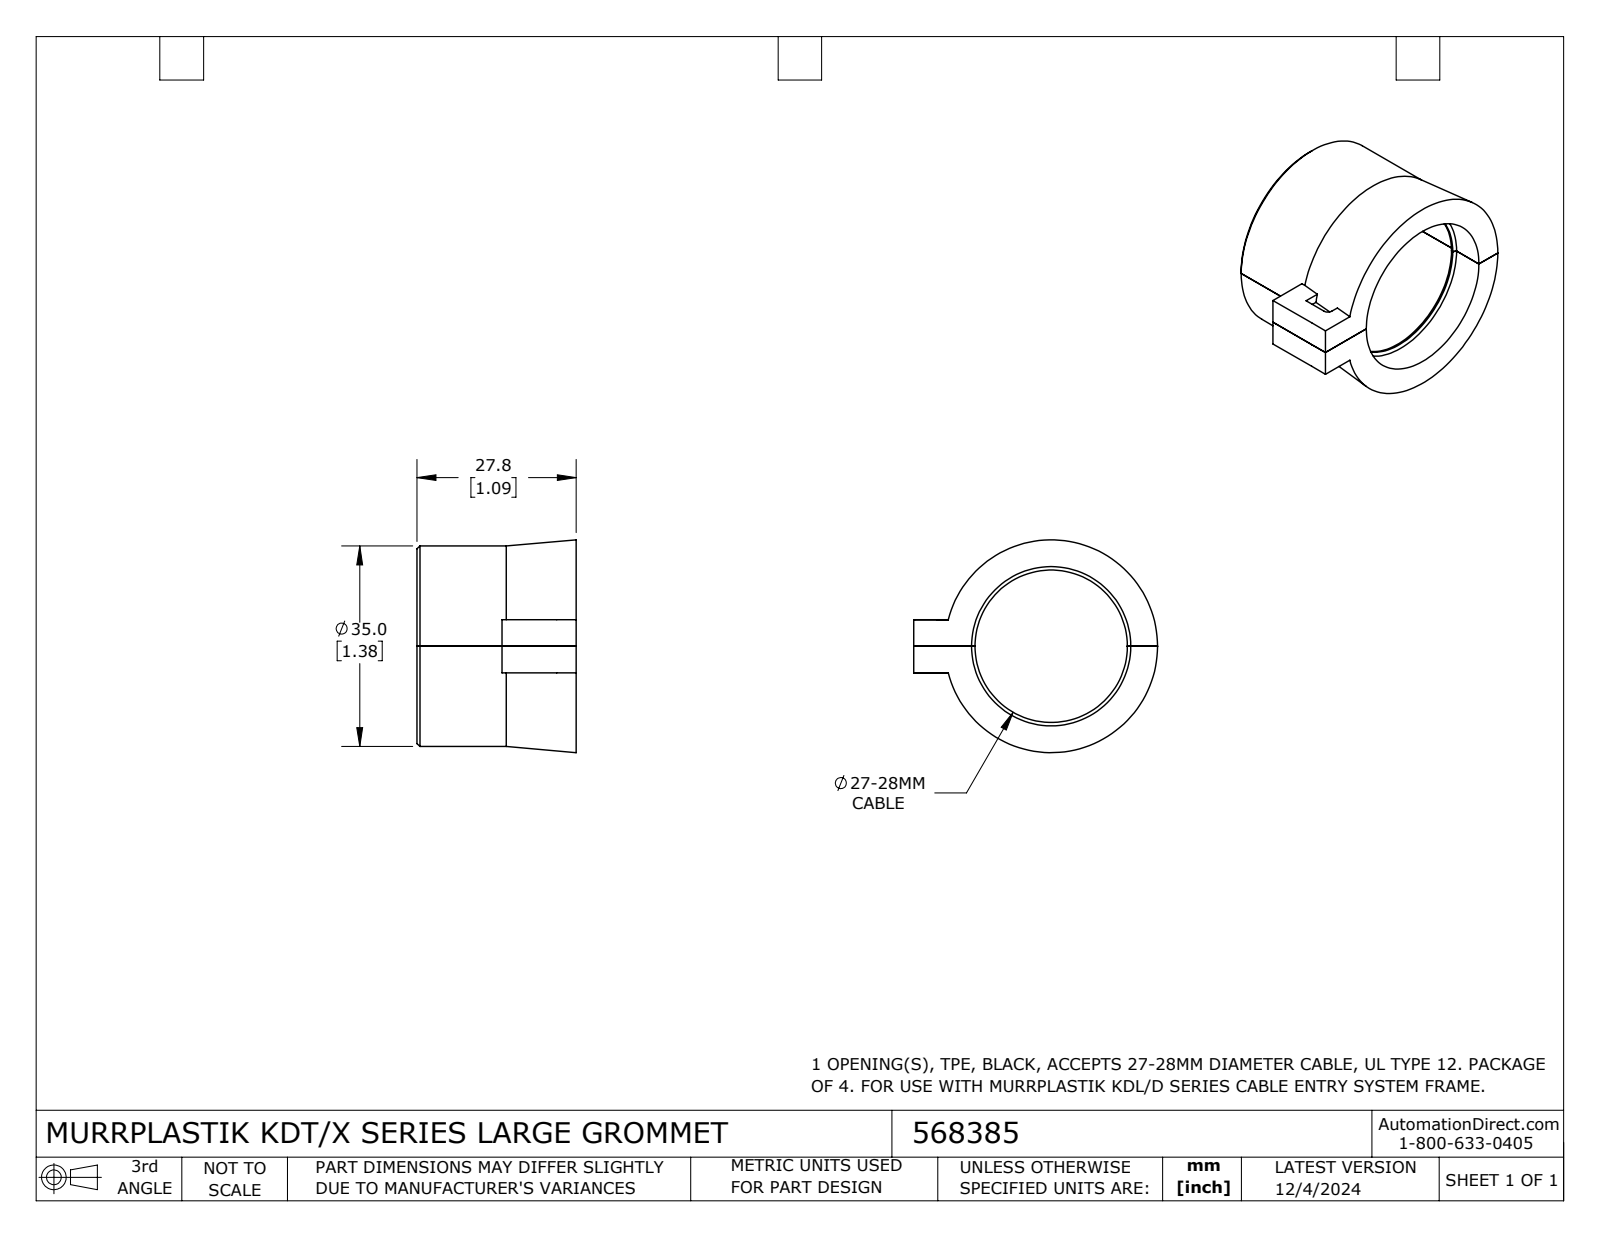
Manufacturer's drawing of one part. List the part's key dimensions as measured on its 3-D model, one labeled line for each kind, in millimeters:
Part name (STEP PRODUCT): 568385
STEP written by: SolidWorks 2024 (AUTOMOTIVE_DESIGN)
Units: millimetres
Bodies: 2 solids, 46 faces (22 planar, 14 cylindrical, 10 other)
Overall size (bounding box): 42.6 × 37.1 × 27.8
Volume: 11 300 mm³ · Surface area: 7 297 mm²
Round holes (diameter × count): ⌀26.6 ×1, ⌀27.8 ×1
Round bosses / shafts (diameter × count): ⌀35 ×1
Partial cylindrical surfaces — rounded edges, fillets, slot ends (radius × count): R0.5 ×4, R1 ×1
Main face-to-face distances: 27.8, 4.6, 9.3, 13, 14.9, 1.5, 7.7, 3.1, 4, 6.2
